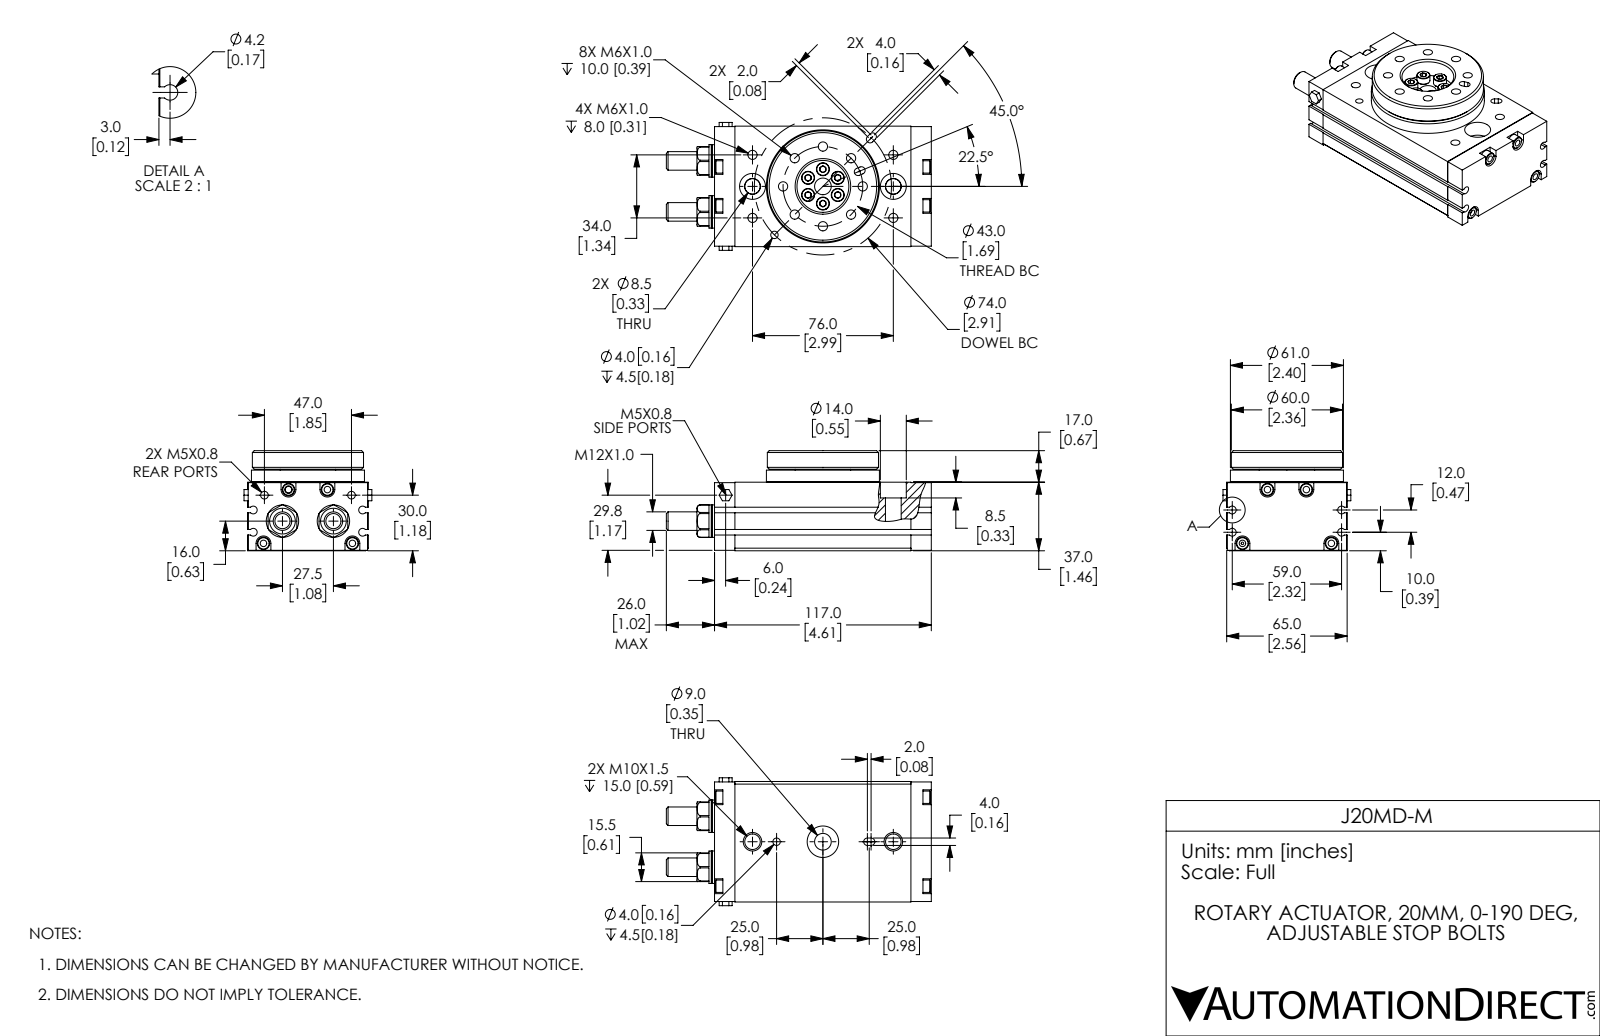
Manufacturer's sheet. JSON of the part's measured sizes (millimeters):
{"part_name": "J20MD-M; J20MD-M_M4_91290A138; J20MD-M_table; J20MD-M_BODY", "step_written_by": "SolidWorks 2017 (AUTOMOTIVE_DESIGN)", "units": "millimeters", "bodies": {"solids": 8, "faces": 695, "planar": 211, "cylindrical": 320, "other": 164}, "overall_size": [143, 69, 54], "volume_mm3": 306094, "surface_area_mm2": 54545, "round_holes": [[5, 8], [3.5, 4], [4.92, 4], [4, 3], [4.13, 2], [8.38, 2], [8.5, 2], [14, 2], [9, 1], [17, 1], [28, 1], [32, 1]], "round_bosses_or_shafts": [[7, 6], [4, 6], [3.09, 6], [6.66, 4], [17.5, 2], [10, 2], [61, 1], [60, 1]], "partial_cylinders_radius": [[2, 6], [2.1, 4], [4, 4]], "face_to_face_distances": [37, 65, 36.75, 7, 6.5, 0.5, 44, 43.5, 17, 10.5], "hole_center_spacings": [16.45, 21.5, 39.72, 9.25, 17, 22.87, 23.69, 27.4]}
